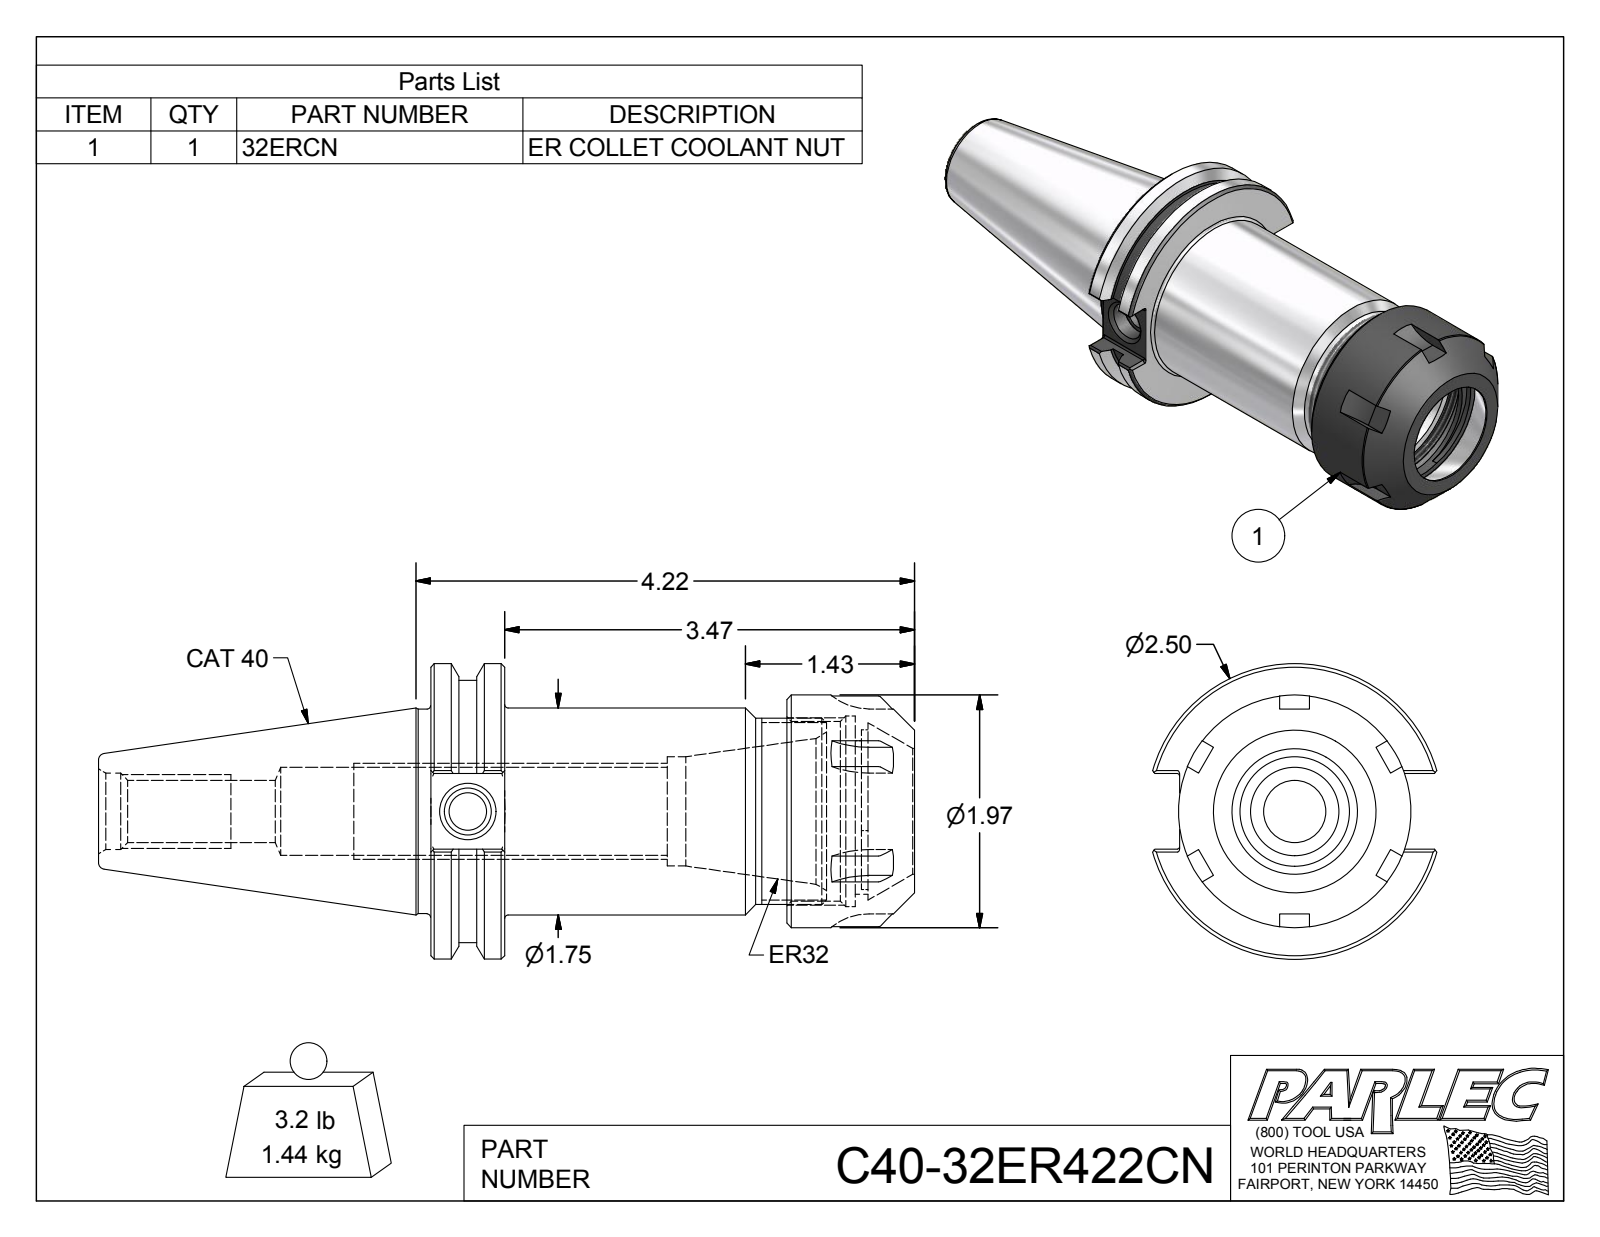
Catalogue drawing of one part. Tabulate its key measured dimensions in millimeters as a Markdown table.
| quantity | value |
| --- | --- |
| part name | C40-32ER422CN; C40-32ER4-1; 32ERCN |
| STEP written by | Autodesk Inventor 2012 (AUTOMOTIVE_DESIGN) |
| units | millimeters |
| bodies | 2 solids, 127 faces (55 planar, 39 cylindrical, 33 other) |
| overall size | 175.5 × 63.5 × 61 |
| volume | 186 200 mm³ |
| surface area | 44 660 mm² |
| round holes (diameter × count) | 8 × 1, 10.1 × 1, 13.4 × 1, 16.5 × 1, 18.9 × 1, 23.5 × 1, 27 × 1, 33 × 1, 38.7 × 1, 41 × 1 |
| round bosses / shafts (diameter × count) | 63.5 × 1, 56.4 × 1, 50 × 1, 44.5 × 1, 43.9 × 1, 40 × 1 |
| partial cylindrical surfaces (radius × count) | 0.5 × 12, 12.7 × 6, 17.5 × 1 |
| main face-to-face distances | 15.9, 76.5, 60.6, 91.2, 75.3, 14.7, 104, 88.1, 27.5, 12.8 |
| hole center spacings | 1.5 |
